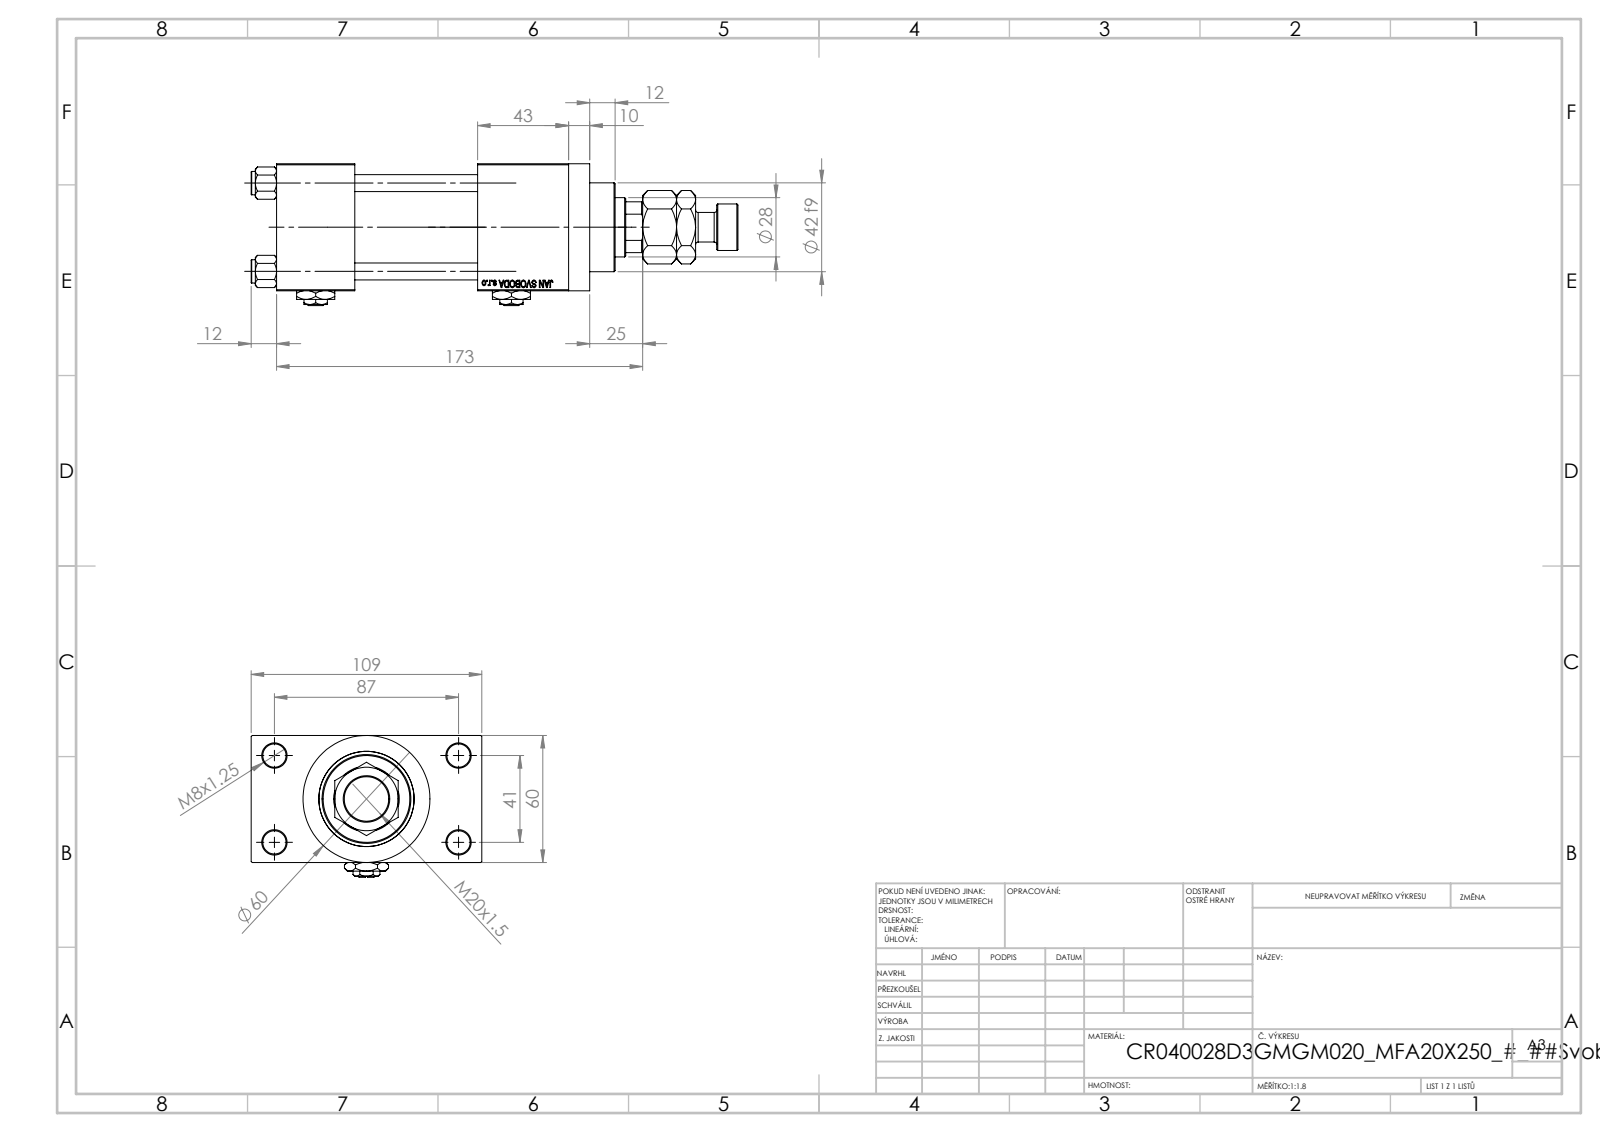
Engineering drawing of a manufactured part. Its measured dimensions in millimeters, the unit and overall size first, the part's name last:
Units: millimetres
Overall size (bounding box): 230 × 109 × 67
Round holes (diameter × count): ⌀8 ×4, ⌀11 ×4, ⌀16.66 ×4, ⌀24 ×4, ⌀7 ×3, ⌀18.5 ×1, ⌀28 ×1, ⌀31 ×1, ⌀40 ×1, ⌀45 ×1
Round bosses / shafts (diameter × count): ⌀11 ×4, ⌀60 ×1, ⌀46 ×1, ⌀42 ×1, ⌀22 ×1, ⌀14 ×1
Partial cylindrical surfaces — rounded edges, fillets, slot ends (radius × count): R13.5 ×1
Main face-to-face distances: 60, 58, 24.5, 84.5, 37, 95, 43, 138, 101, 109
Hole centre spacings: 22.65, 29.49, 41.7, 47.15, 48.09, 64.35, 76.49, 41
Volume: 551 649 mm³ · Surface area: 137 253 mm²
Bodies: 14 solids, 1257 faces (562 planar, 103 cylindrical, 592 other)
Part name (STEP PRODUCT): V215CR_D_Body; V215_VC_A; V215CR_VCP_D; MFA (+3 more)
STEP written by: SolidWorks 2019 (CONFIG_CONTROL_DESIGN)
